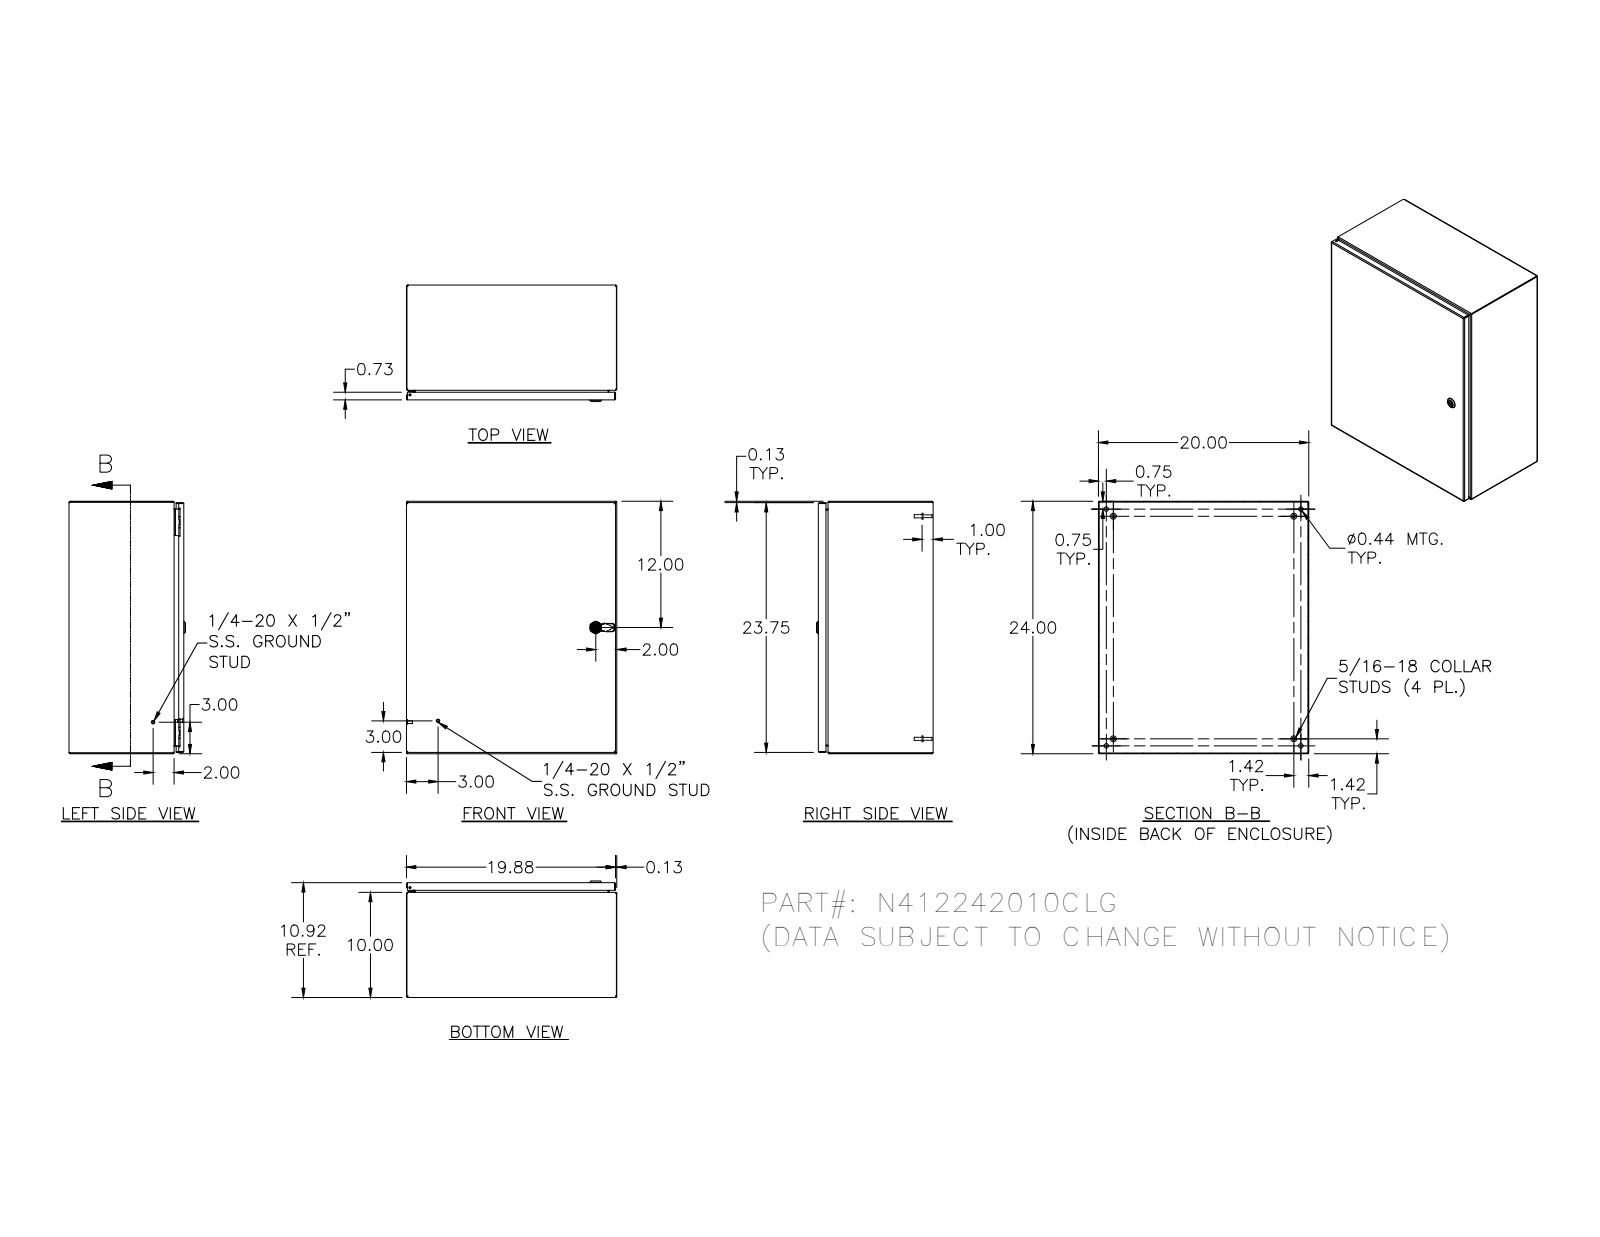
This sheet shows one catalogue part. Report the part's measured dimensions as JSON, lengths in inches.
{"part_name": "N412242010CLG", "step_written_by": "SolidWorks 2018 (AUTOMOTIVE_DESIGN)", "units": "inches", "bodies": {"solids": 33, "faces": 1449, "planar": 530, "cylindrical": 547, "other": 372}, "overall_size": [24, 20, 11.075], "volume_in3": 149.2, "surface_area_in2": 4053, "round_holes": [[0.188, 5], [0.093, 4], [0.152, 4], [0.167, 4], [0.172, 4], [0.437, 4], [0.156, 2], [0.187, 1], [0.197, 1], [0.315, 1], [0.394, 1], [0.402, 1]], "round_bosses_or_shafts": [[0.25, 10], [0.563, 4], [0.36, 4], [0.32, 4], [0.3, 4], [0.256, 4], [0.164, 4], [0.131, 4]], "partial_cylinders_radius": [[0.012, 30], [0.031, 30], [0.05, 26], [0.105, 20], [0.016, 18], [0.125, 16], [0.02, 13], [0.032, 8]], "face_to_face_distances": [0.074, 10.843, 10.769, 10.917, 0.074, 19.926, 20, 19.852, 19.926, 23.852], "hole_center_spacings": [20, 0.66, 0.656, 1.307, 1.965, 18.872, 0.5, 0.984]}
